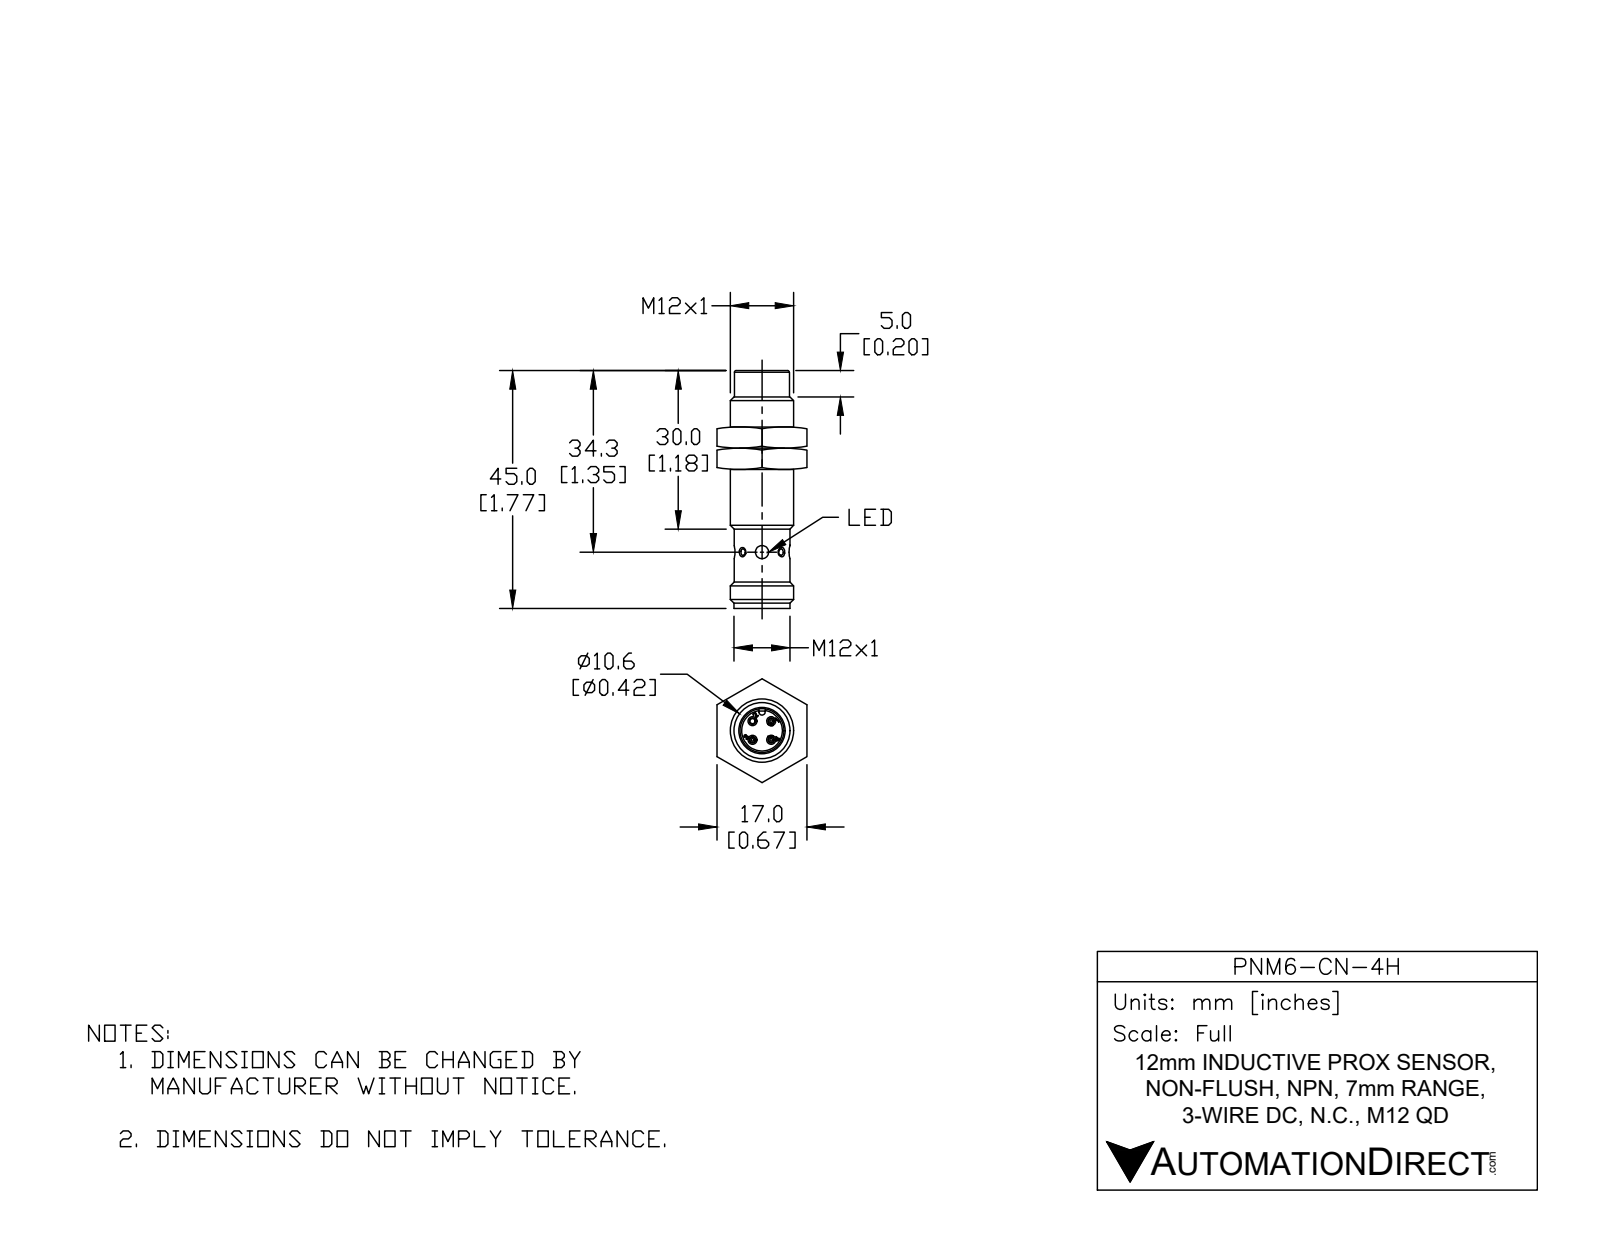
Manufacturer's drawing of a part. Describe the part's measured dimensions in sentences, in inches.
The part is named "PNM6-CN-4H". Its 3-D file was written by "SolidWorks 2017 (AUTOMOTIVE_DESIGN)". It is 1 solid with 491 faces: 117 planar, 138 cylindrical and 236 other. Overall it measures 1.772 by 0.472 by 0.472 inches. Its volume is 0.247 cubic inches and its surface area 8.016 square inches. Round holes: 3 of diameter 0.043, 2 of diameter 0.04, 2 of diameter 0.098, 1 of diameter 0.038, 1 of diameter 0.04, 1 of diameter 0.327, 1 of diameter 0.394, 1 of diameter 0.401. Round bosses or shafts: 6 of diameter 0.039, 1 of diameter 0.472, 1 of diameter 0.417, 1 of diameter 0.415, 1 of diameter 0.4, 1 of diameter 0.392, 1 of diameter 0.39, 1 of diameter 0.38. Partial cylindrical surfaces (rounded edges, fillets, slot ends): 36 of radius 0.004, 6 of radius 0.079, 1 of radius 0.024, 1 of radius 0.031, 1 of radius 0.161. The main face-to-face distances are 0.118, 1.299, 1.181, 0.018, 0.1, 1.281, 1.303, 1.421, 1.404, 0.122. The hole center spacings are 0.098, 0.139, 0.197.
